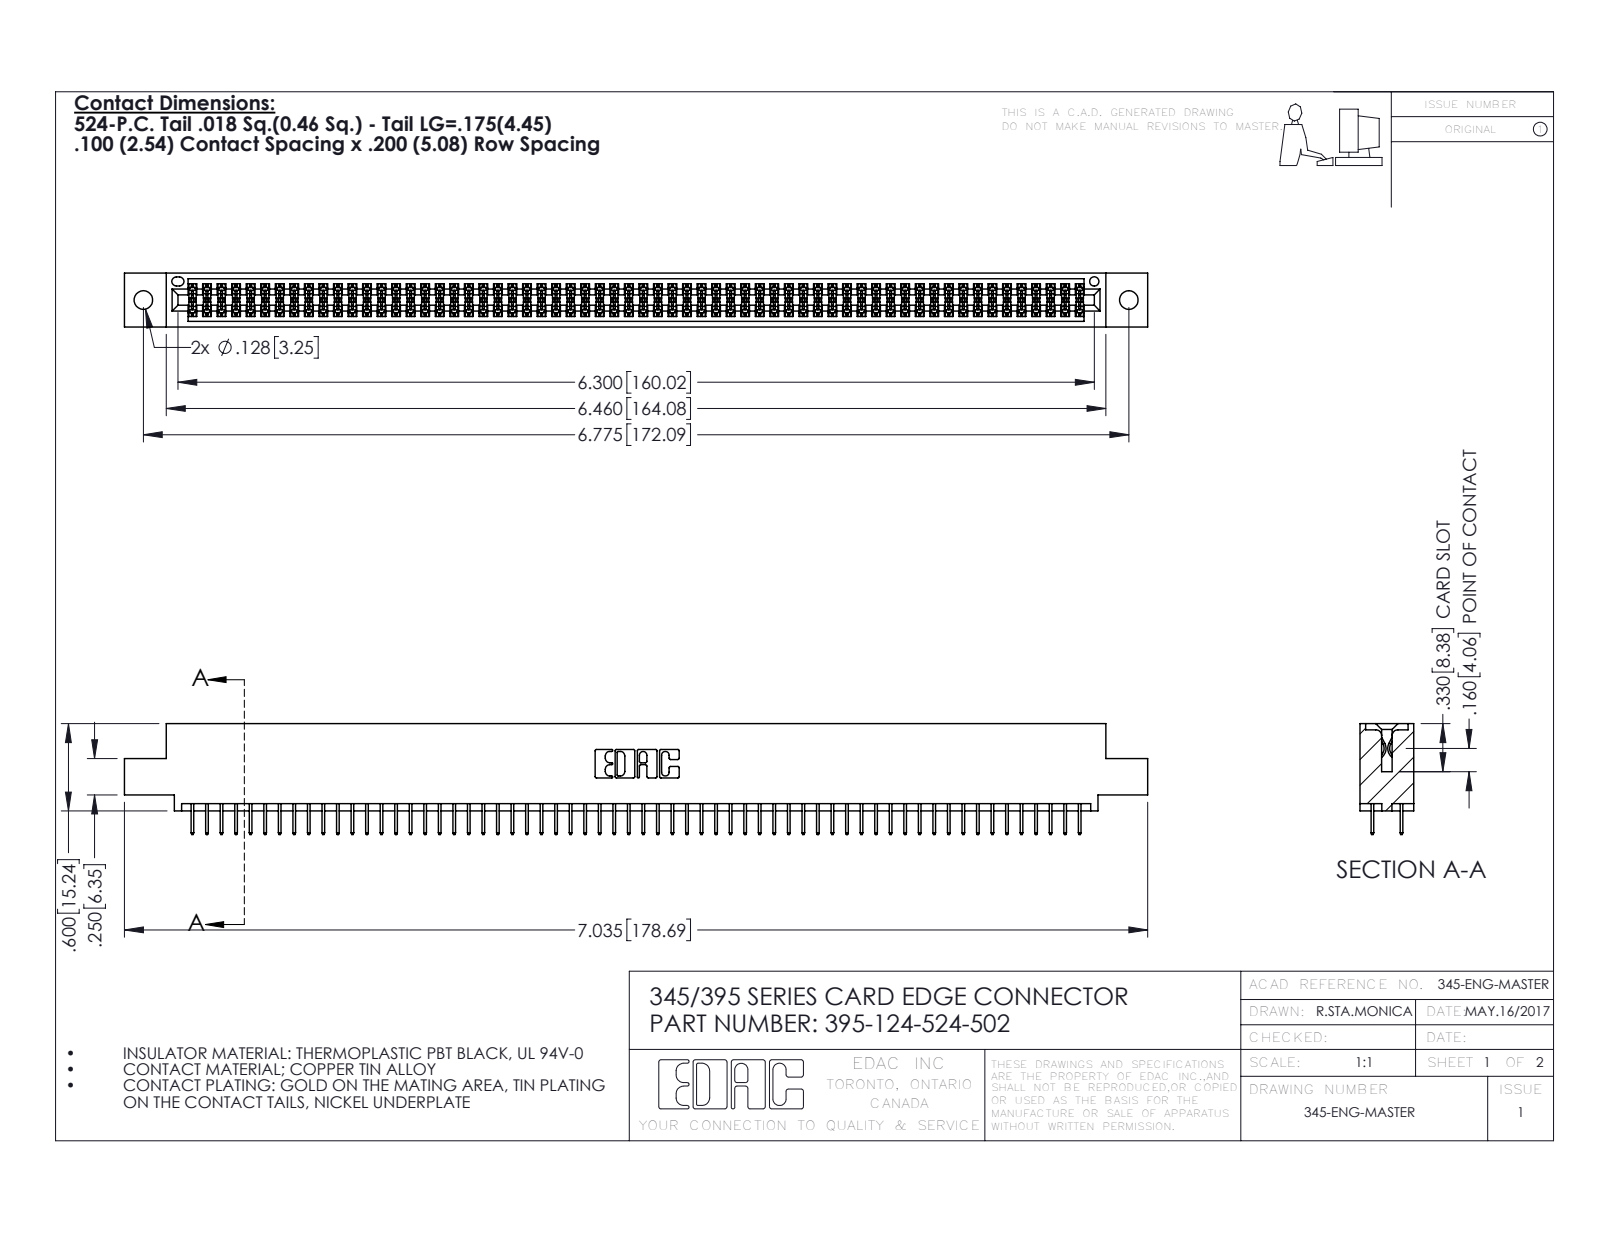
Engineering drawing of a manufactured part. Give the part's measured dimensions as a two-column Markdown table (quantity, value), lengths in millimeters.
| quantity | value |
| --- | --- |
| part name | 395-124-524-502; 345-292-001_345-293-124; 345 Part_0.110 Offset - 0.128 Dia |
| STEP written by | SolidWorks 2016 (CONFIG_CONTROL_DESIGN) |
| units | millimeters |
| bodies | 125 solids, 6826 faces (4920 planar, 1906 cylindrical, 0 other) |
| overall size | 178.7 × 19.4 × 9.4 |
| volume | 17 240 mm³ |
| surface area | 25 210 mm² |
| round holes (diameter × count) | 3.3 × 2, 1.6 × 1 |
| partial cylindrical surfaces (radius × count) | 0.2 × 186, 0.3 × 22, 0.2 × 6, 0.8 × 6, 0.7 × 3, 0.4 × 2, 0.5 × 2, 0.6 × 2 |
| main face-to-face distances | 1.8, 7.6, 5.1, 9.4, 2.5, 6.9, 0.6, 5.7, 1.8, 4.4 |
| hole center spacings | 6.9, 166.1, 172.1 |
